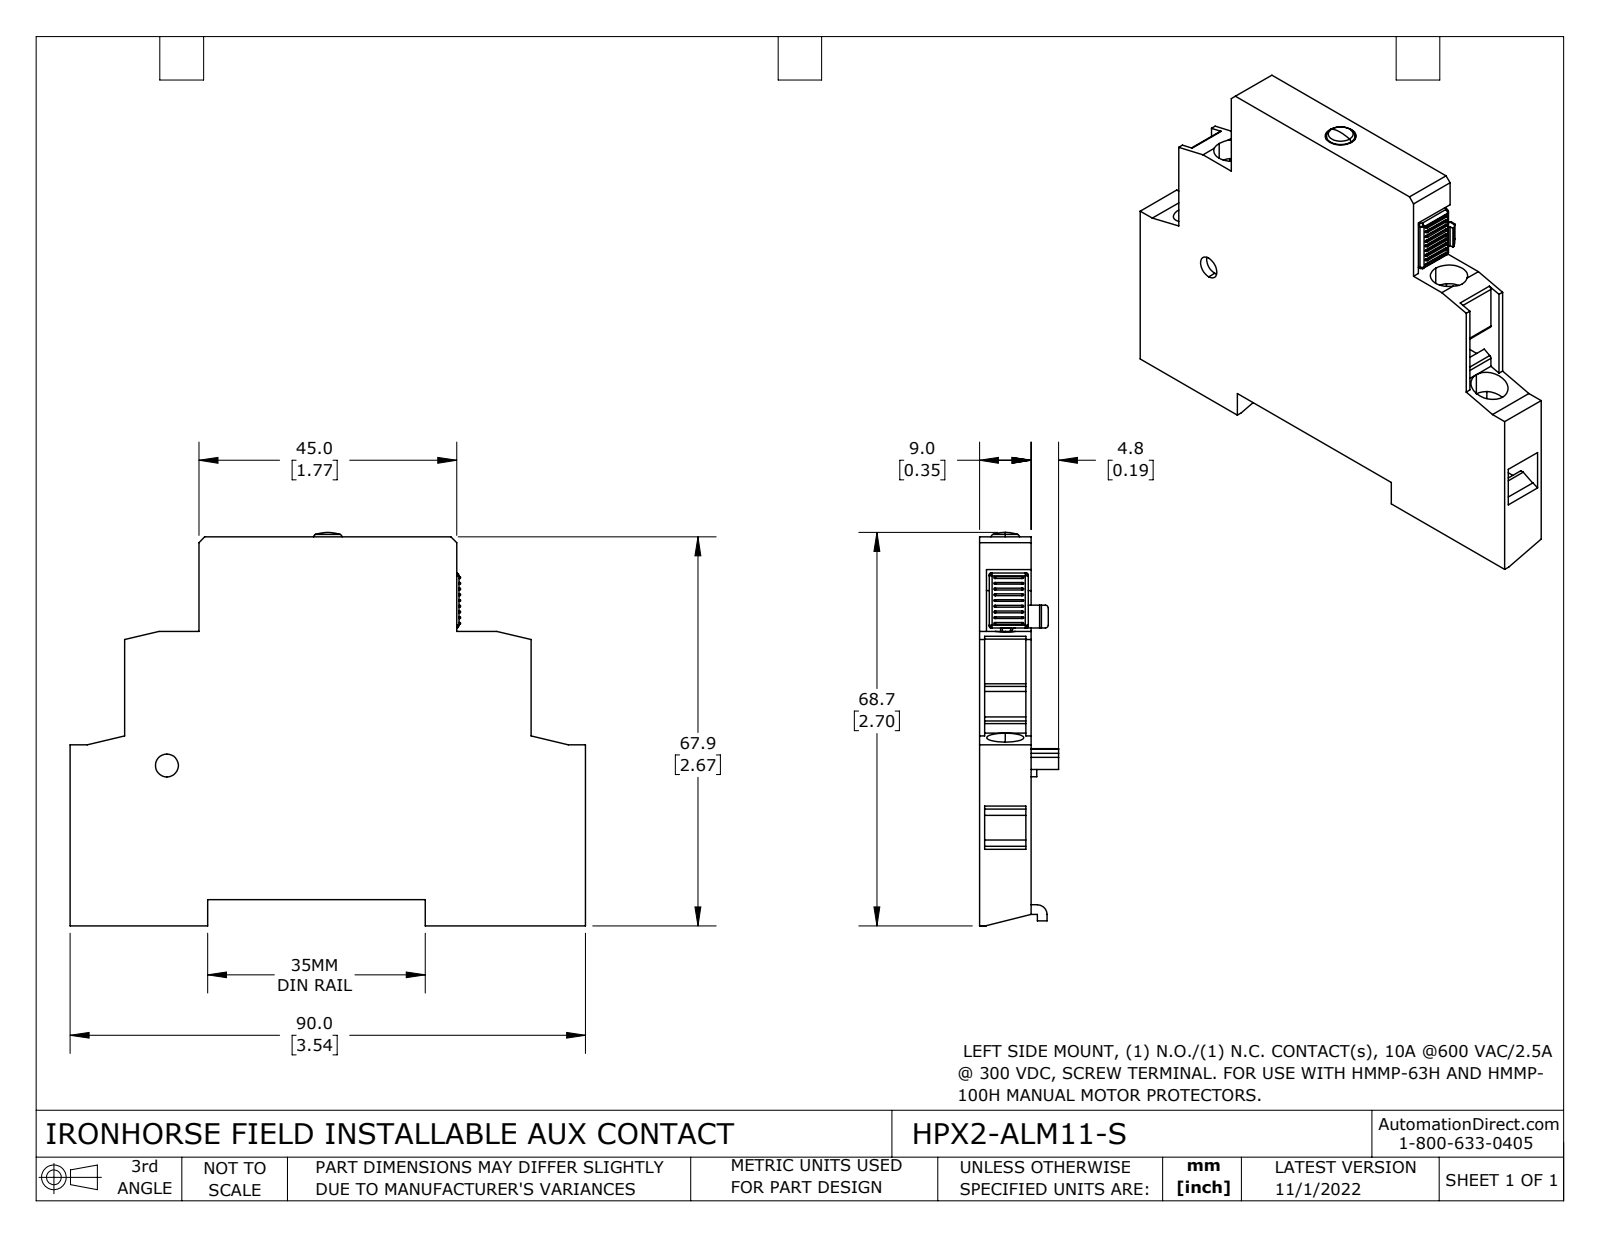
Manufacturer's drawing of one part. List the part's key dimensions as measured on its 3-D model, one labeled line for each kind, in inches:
Part name (STEP PRODUCT): HPX2-ALM11-S
STEP written by: SolidWorks 2021 (CONFIG_CONTROL_DESIGN)
Units: inches
Bodies: 4 solids, 312 faces (194 planar, 75 cylindrical, 43 other)
Overall size (bounding box): 3.543 × 2.704 × 0.543
Volume: 2.306 in³ · Surface area: 24.35 in²
Round holes (diameter × count): ⌀0.256 ×4, ⌀0.157 ×1, ⌀0.213 ×1
Round bosses / shafts (diameter × count): ⌀0.197 ×2, ⌀0.079 ×2, ⌀0.154 ×1
Partial cylindrical surfaces — rounded edges, fillets, slot ends (radius × count): R0.02 ×17, R0.006 ×9, R0.012 ×8, R0.039 ×8, R0.028 ×2, R0.047 ×1, R0.067 ×1, R0.071 ×1
Main face-to-face distances: 0.354, 0.035, 0.319, 0.283, 0.394, 0.886, 2.657, 2.492, 0.492, 3.051
Hole centre spacings: 0.394, 1.053, 1.447, 2.5, 2.106, 2.894
